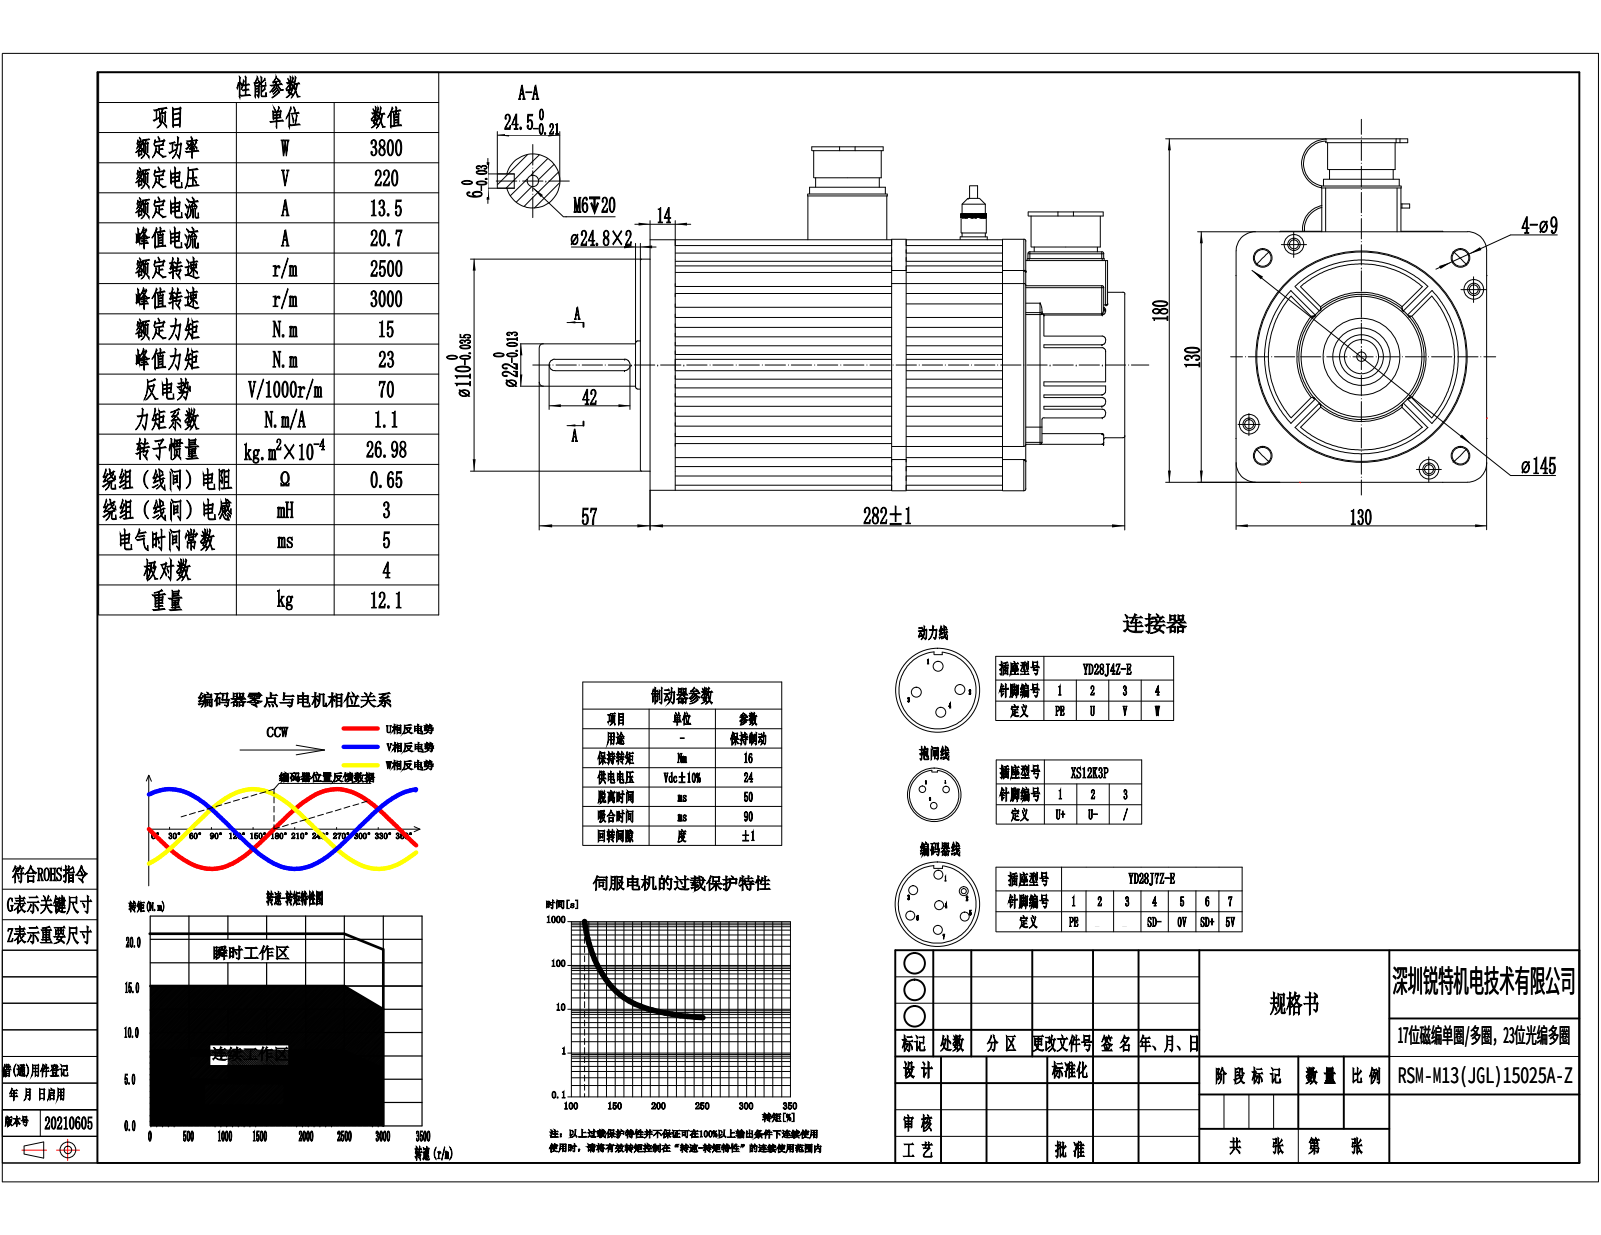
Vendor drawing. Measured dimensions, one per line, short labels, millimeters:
name: 编码器罩盖
written by: SolidWorks 2013 (CONFIG_CONTROL_DESIGN)
unit: mm
bodies: 9 solids, 2229 faces (1290 planar, 684 cylindrical, 255 other)
size: 344.4 × 178.25 × 130.5
volume: 1 149 000 mm³; area: 599 927 mm²
holes: 11× ⌀3.5, 7× ⌀5, 6× ⌀2.5, 6× ⌀6.6, 5× ⌀3.3, 5× ⌀4, 5× ⌀10.5, 4× ⌀9, 2× ⌀23.5, 2× ⌀30, 2× ⌀32.5, 1× ⌀5.25
bosses: 4× ⌀7, 2× ⌀39, 2× ⌀36, 2× ⌀32.8, 2× ⌀28, 2× ⌀27, 1× ⌀123.5, 1× ⌀122.35
rounds: 164× R1, 9× R3, 8× R30.29, 4× R2, 4× R2.25, 4× R5, 4× R10, 2× R4
face distances: 5.4, 1.8, 77.5, 72.4, 7, 10.6, 61.8, 3.6, 67, 56.4
hole spacings: 20.86, 29.5, 30, 109.75, 26.26, 41.72, 42.43, 68
